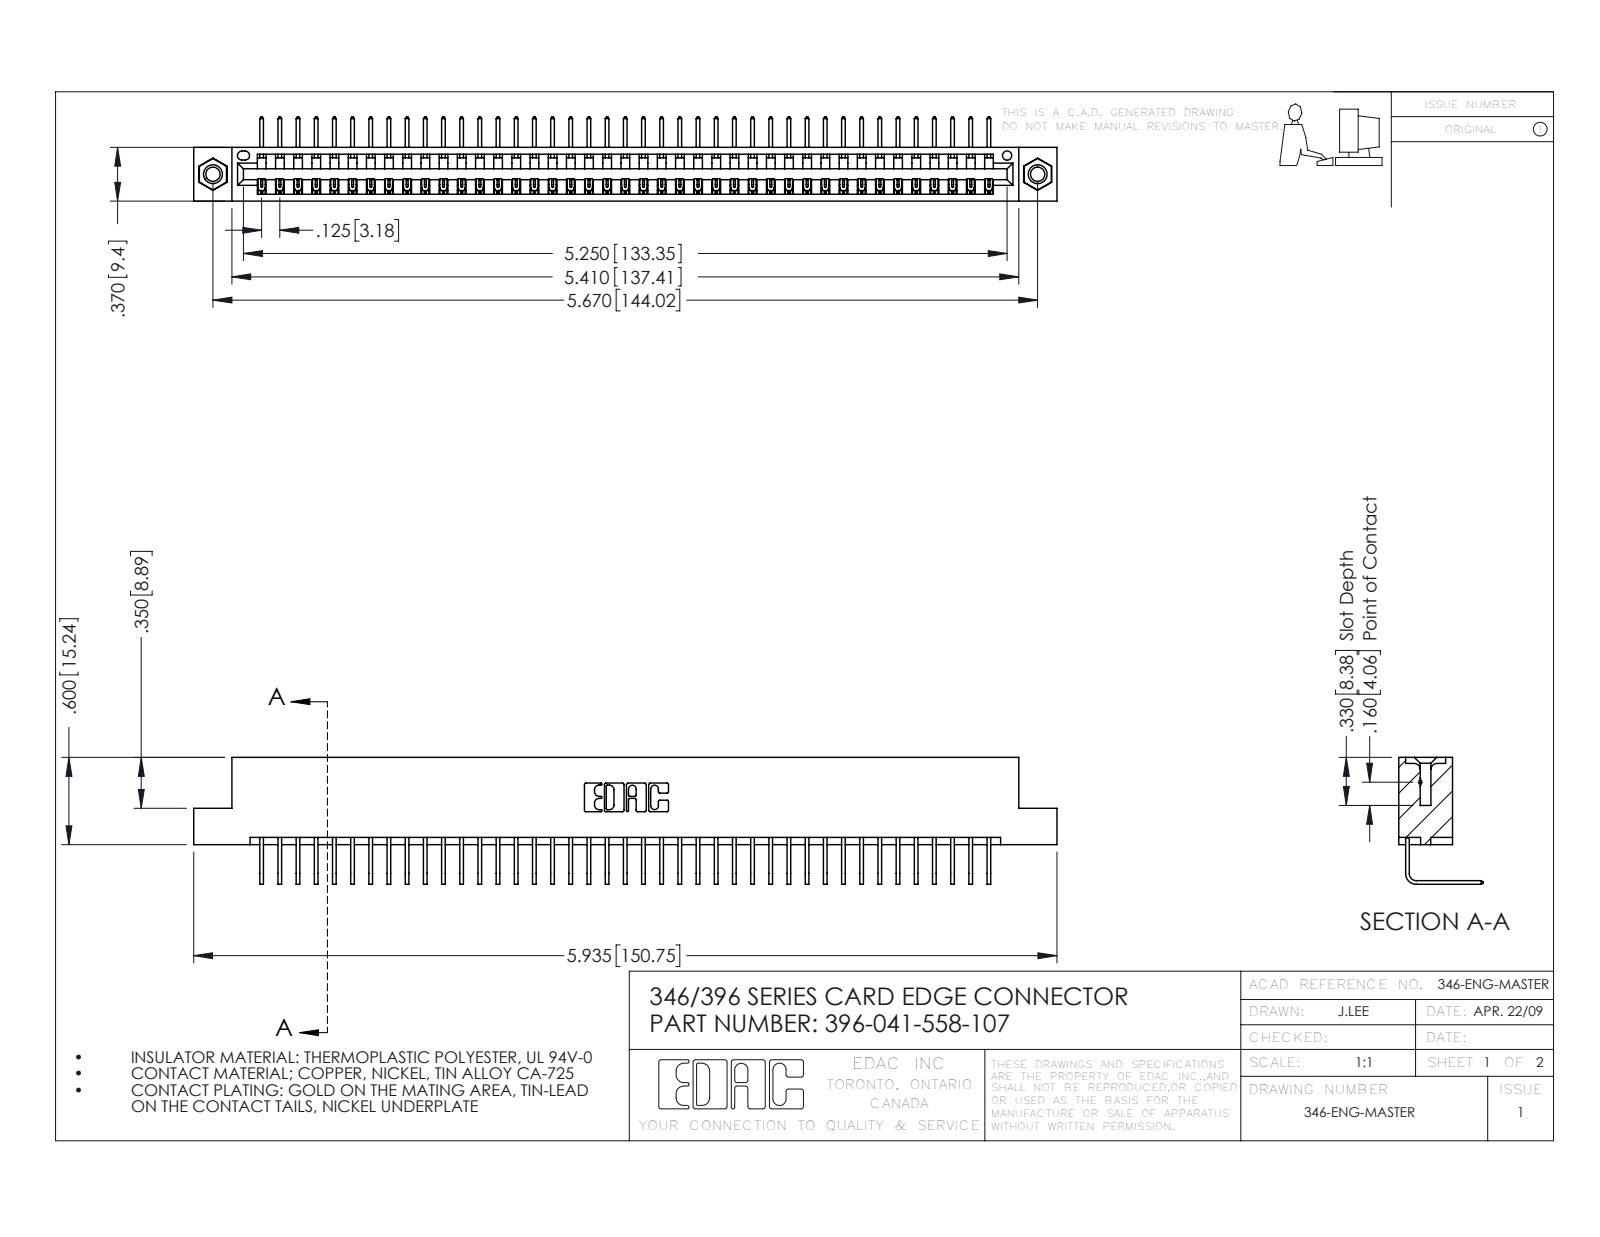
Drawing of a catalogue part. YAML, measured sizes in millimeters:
part_name: "345-292-001_558 Tail - 2; 346 Part_Flush Mounting Lugs - 0.156 Dia-TI; 396-041-558-107; 345-250-001_345-250-005-103"
step_written_by: "SolidWorks 2016 (CONFIG_CONTROL_DESIGN)"
units: millimeters
bodies: {solids: 44, faces: 2642, planar: 1830, cylindrical: 796, other: 16}
overall_size: [150.7, 22.2, 14.7]
volume: 14600
surface_area: 19020
round_holes:
  - {diameter: 2.5, count: 2}
  - {diameter: 3.2, count: 2}
  - {diameter: 4, count: 2}
  - {diameter: 1.6, count: 1}
round_bosses_or_shafts:
  - {diameter: 3.9, count: 2}
partial_cylinders:
  - {radius: 0.2, count: 82}
  - {radius: 0.3, count: 22}
  - {radius: 0.2, count: 6}
  - {radius: 0.8, count: 6}
  - {radius: 0.7, count: 3}
  - {radius: 0.8, count: 2}
  - {radius: 1, count: 2}
  - {radius: 0.4, count: 1}
face_to_face_distances: [8.2, 1.2, 9.4, 6.4, 7.6, 0.6, 1.8, 3.8, 5.6, 2.5]
hole_center_spacings: [6.2, 138.7, 144]
